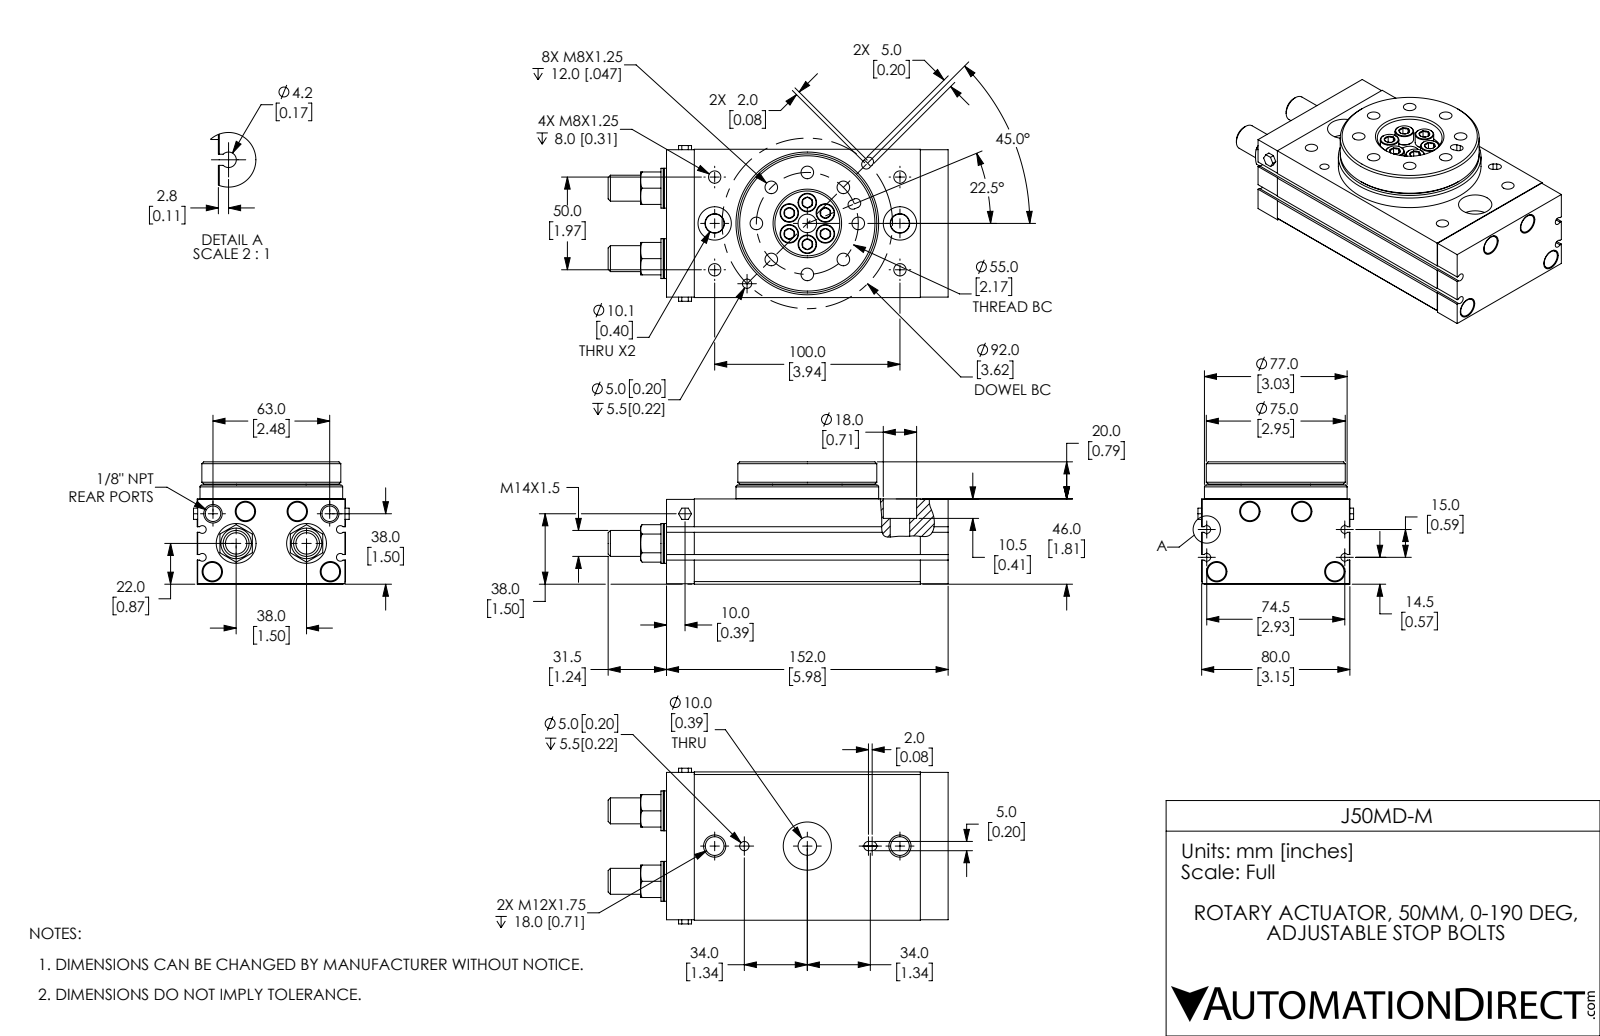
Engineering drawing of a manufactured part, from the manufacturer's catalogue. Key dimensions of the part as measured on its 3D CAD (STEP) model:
Part name (STEP PRODUCT): J50MD-M; J50MD-M_M6_91290A310; J50MD-M_table; J50MD-M_body2
STEP written by: SolidWorks 2017 (AUTOMOTIVE_DESIGN)
Units: millimetres
Bodies: 8 solids, 605 faces (181 planar, 282 cylindrical, 142 other)
Overall size (bounding box): 183.5 × 84 × 66
Volume: 614 337 mm³ · Surface area: 85 843 mm²
Round holes (diameter × count): ⌀6.8 ×8, ⌀6 ×4, ⌀6.65 ×4, ⌀11 ×4, ⌀8.38 ×2, ⌀10.11 ×2, ⌀10.5 ×2, ⌀18 ×2, ⌀10 ×1, ⌀26 ×1, ⌀35 ×1, ⌀38 ×1
Round bosses / shafts (diameter × count): ⌀10 ×10, ⌀6 ×6, ⌀4.7 ×6, ⌀21.5 ×2, ⌀14 ×2, ⌀77 ×1, ⌀75 ×1, ⌀37.5 ×1
Partial cylindrical surfaces — rounded edges, fillets, slot ends (radius × count): R2.5 ×6, R2.1 ×4
Main face-to-face distances: 46, 45.75, 80, 7.5, 12, 53.5, 8, 12.5, 54, 0.5
Hole centre spacings: 21.05, 50.82, 11.25, 18.63, 25, 27.5, 27.51, 31.05
